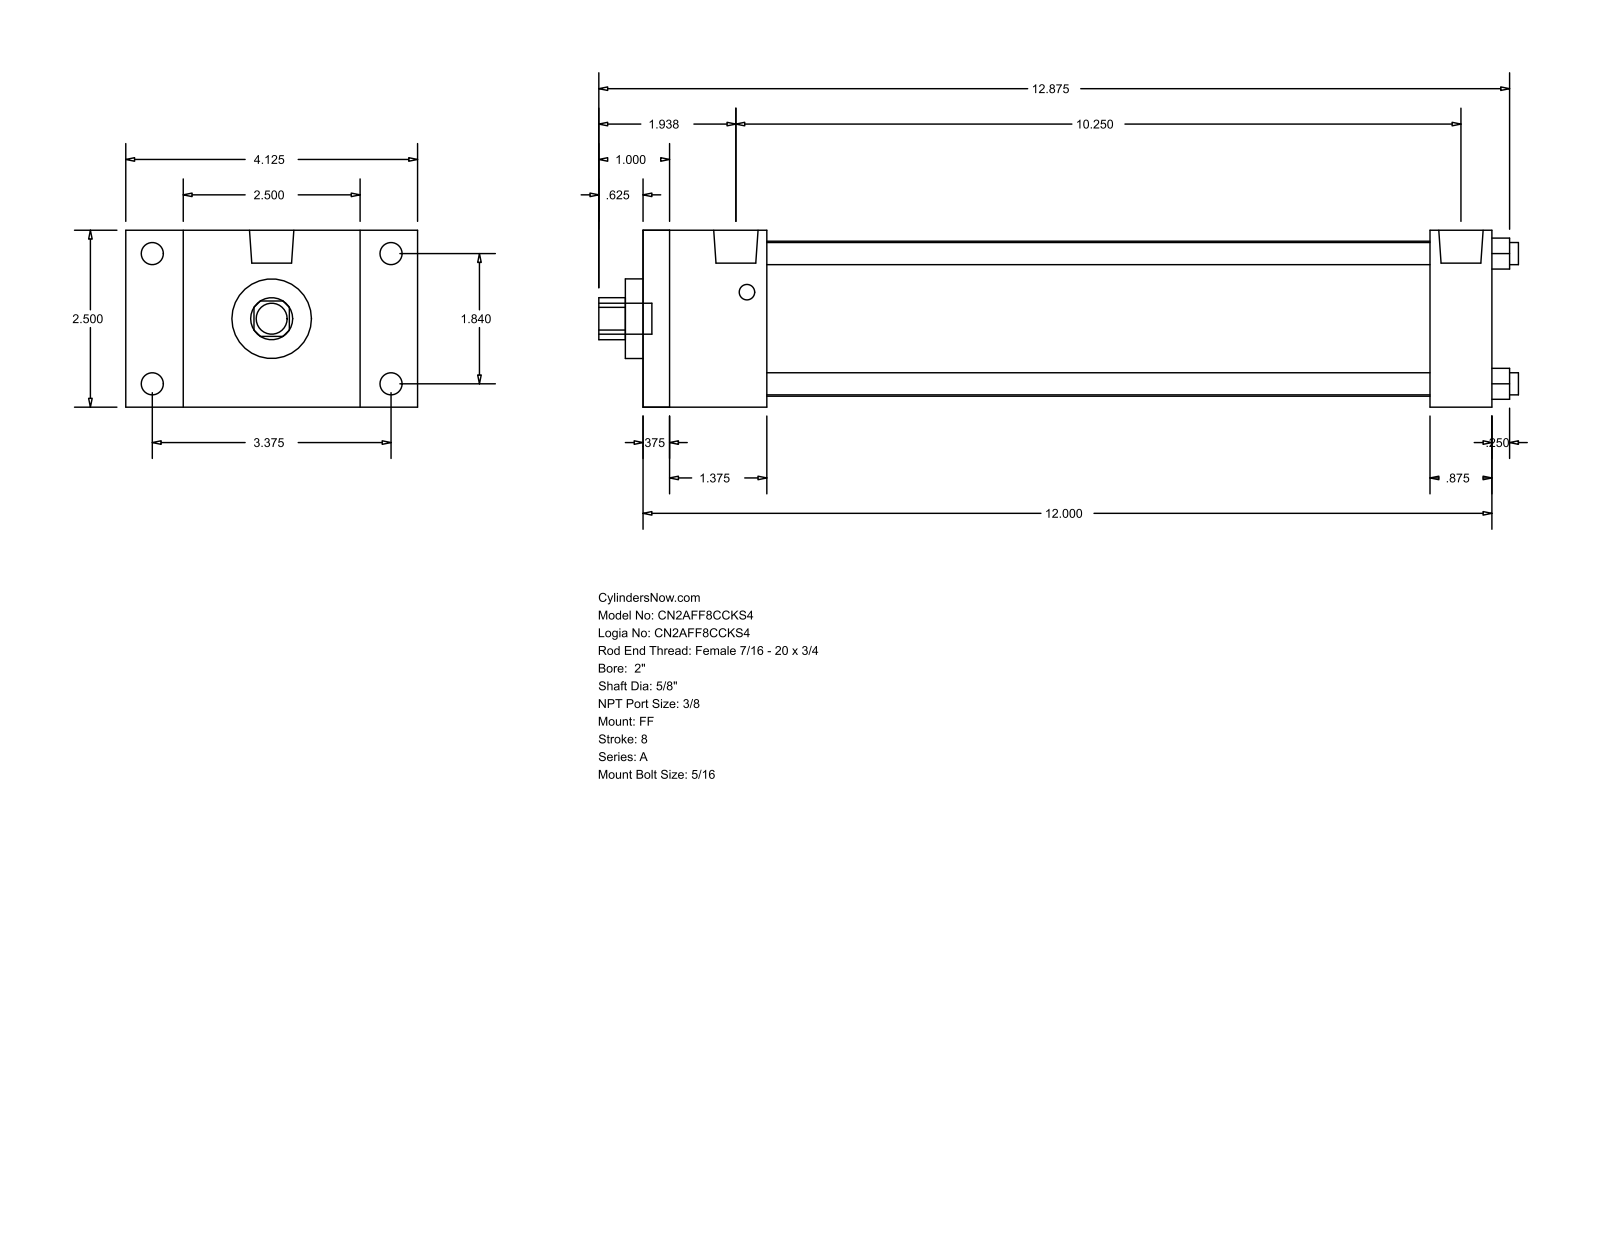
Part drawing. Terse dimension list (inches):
name: A_FF__0200_0.625
written by: GSSL Pune (CONFIG_CONTROL_DESIGN)
unit: in
bodies: 0 solids, 92 faces (64 planar, 28 cylindrical, 0 other)
size: 13 × 4.125 × 2.5
holes: 4× ⌀0.313, 1× ⌀0.625, 1× ⌀1.125, 1× ⌀2.19
bosses: 4× ⌀0.313, 4× ⌀0.219, 2× ⌀0.627, 1× ⌀0.437
rounds: 1× R0.297
face distances: 2.5, 12, 0.375, 11.625, 1.75, 11.125, 1.375, 10.75, 9.375, 10.25
hole spacings: 1.301, 1.84, 2.602
